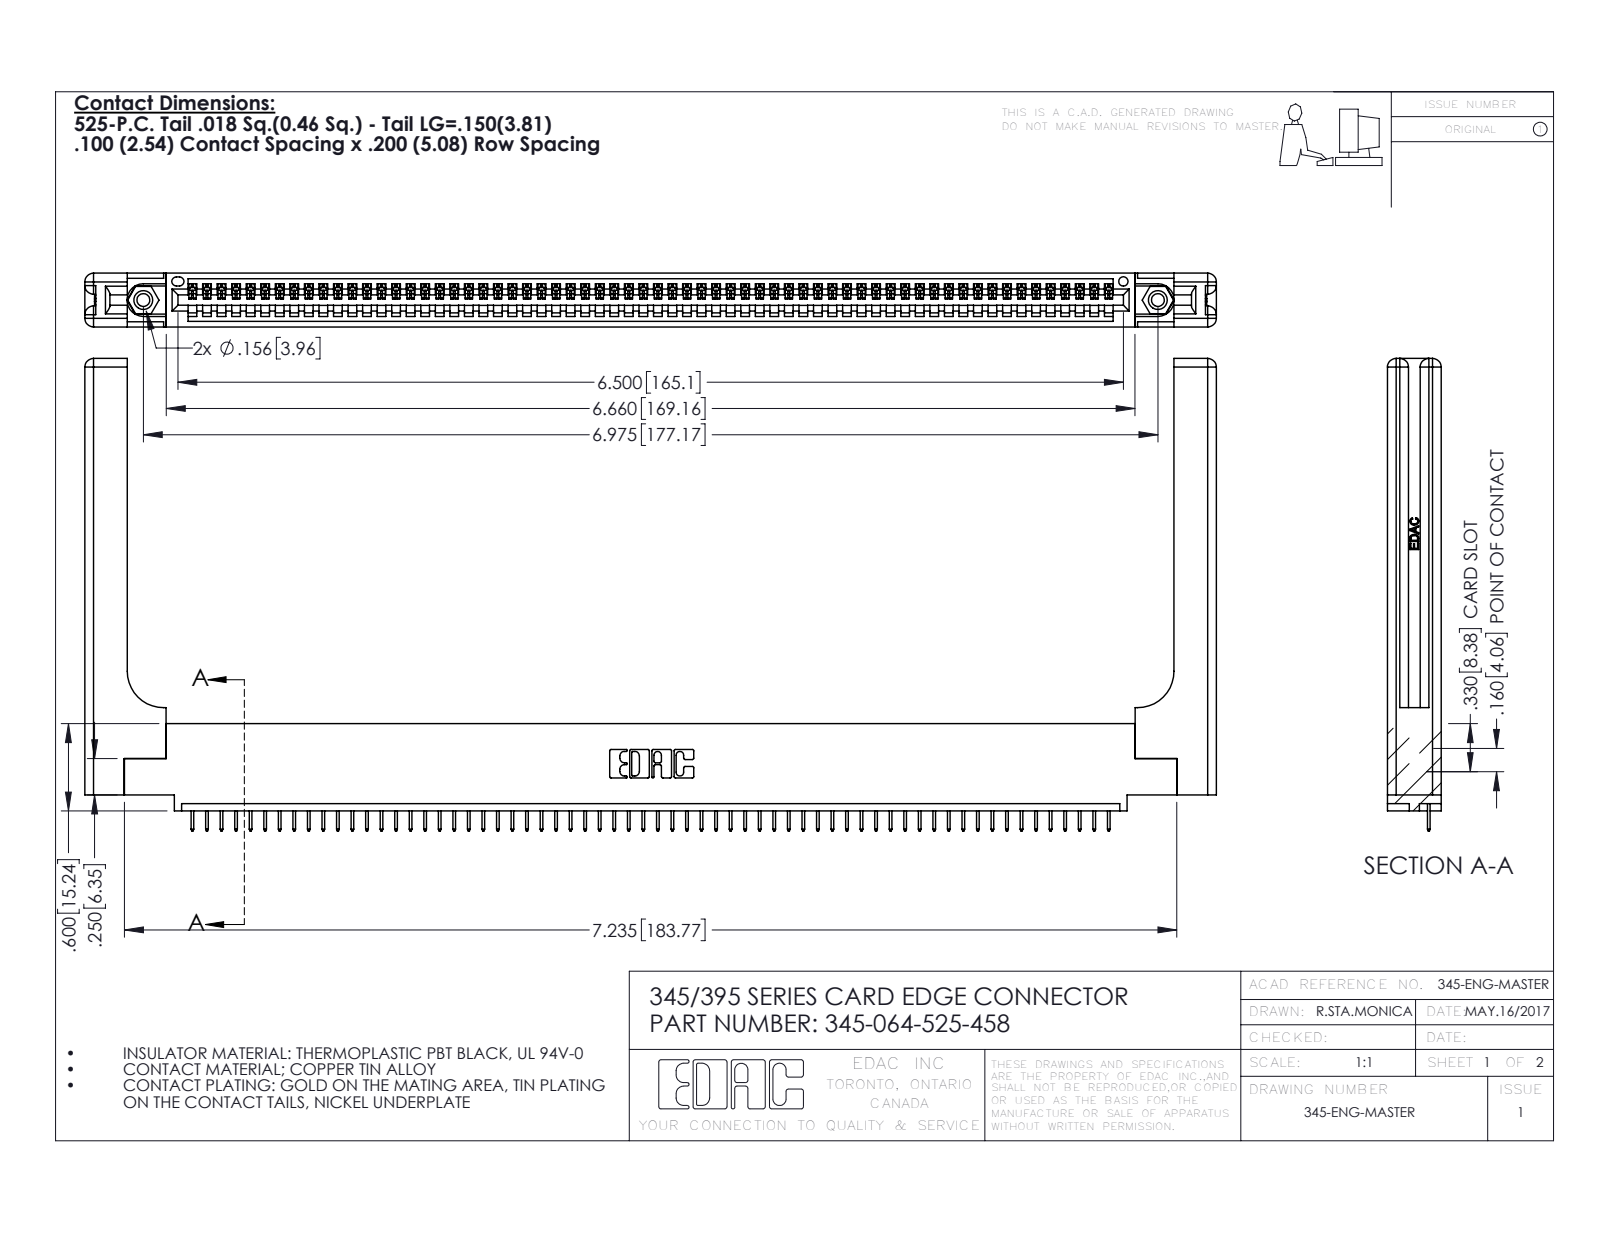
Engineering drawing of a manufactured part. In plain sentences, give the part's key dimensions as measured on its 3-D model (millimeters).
The part is named "345-064-525-458; 345-220-058_345-220-058; 345 Part_0.110 Offset - 0.156 Dia-TH; 345-292-001_345-293-125 (+1 more)". Its 3-D file was written by "SolidWorks 2020 (CONFIG_CONTROL_DESIGN)". It is 69 solids with 4354 faces: 3176 planar, 1118 cylindrical and 60 other. Overall it measures 197.6 by 82.5 by 9.4 millimeters. Its volume is 27 120 cubic millimeters and its surface area 29 550 square millimeters. Round holes: 2 of diameter 2.3, 2 of diameter 3.2, 2 of diameter 4, 1 of diameter 1.6. Round bosses or shafts: 2 of diameter 3.9. Partial cylindrical surfaces (rounded edges, fillets, slot ends): 128 of radius 0.2, 22 of radius 0.3, 16 of radius 1.5, 6 of radius 0.2, 6 of radius 0.8, 3 of radius 0.7, 2 of radius 0.8, 2 of radius 0.8. The main face-to-face distances are 1.8, 9.4, 7.6, 2.5, 6.9, 0.6, 5.1, 5.7, 3.8, 3.8. The hole center spacings are 6.9, 171.2, 177.2.
